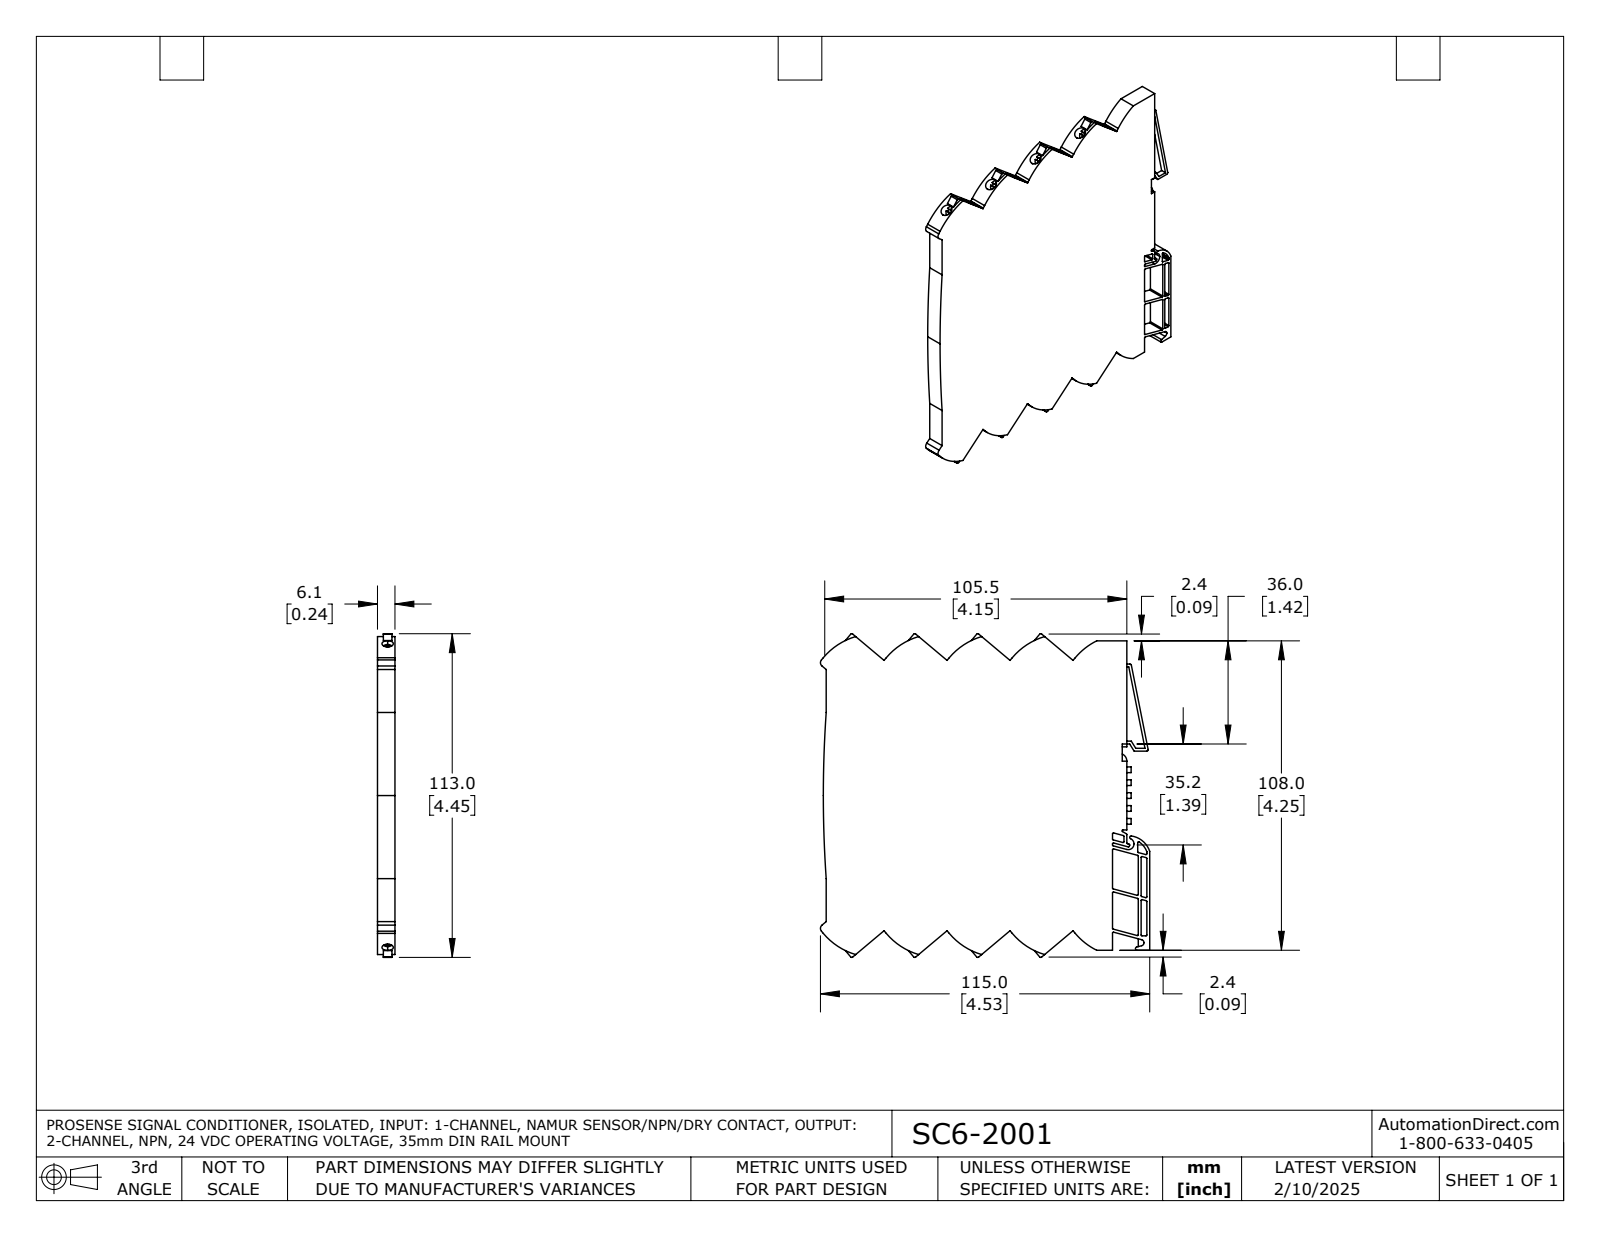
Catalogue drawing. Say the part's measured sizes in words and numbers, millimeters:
The part is named "SC6-2001". Its 3-D file was written by "SolidWorks 2021 (AUTOMOTIVE_DESIGN)". It is 1 solid with 457 faces: 333 planar, 124 cylindrical and 0 other. Overall it measures 115 by 113 by 6.1 millimeters. Its volume is 65 480 cubic millimeters and its surface area 28 500 square millimeters. Round holes: 8 of diameter 4. Partial cylindrical surfaces (rounded edges, fillets, slot ends): 32 of radius 0.3, 11 of radius 0.5, 10 of radius 1.5, 10 of radius 23.3, 1 of radius 0.6, 1 of radius 1.1, 1 of radius 1.5, 1 of radius 1.8. The main face-to-face distances are 6.1, 1, 3, 4, 2.1, 14.1, 4, 16.8, 1, 2. The hole center spacings are 14.1, 28.3, 14.1, 42.4.
